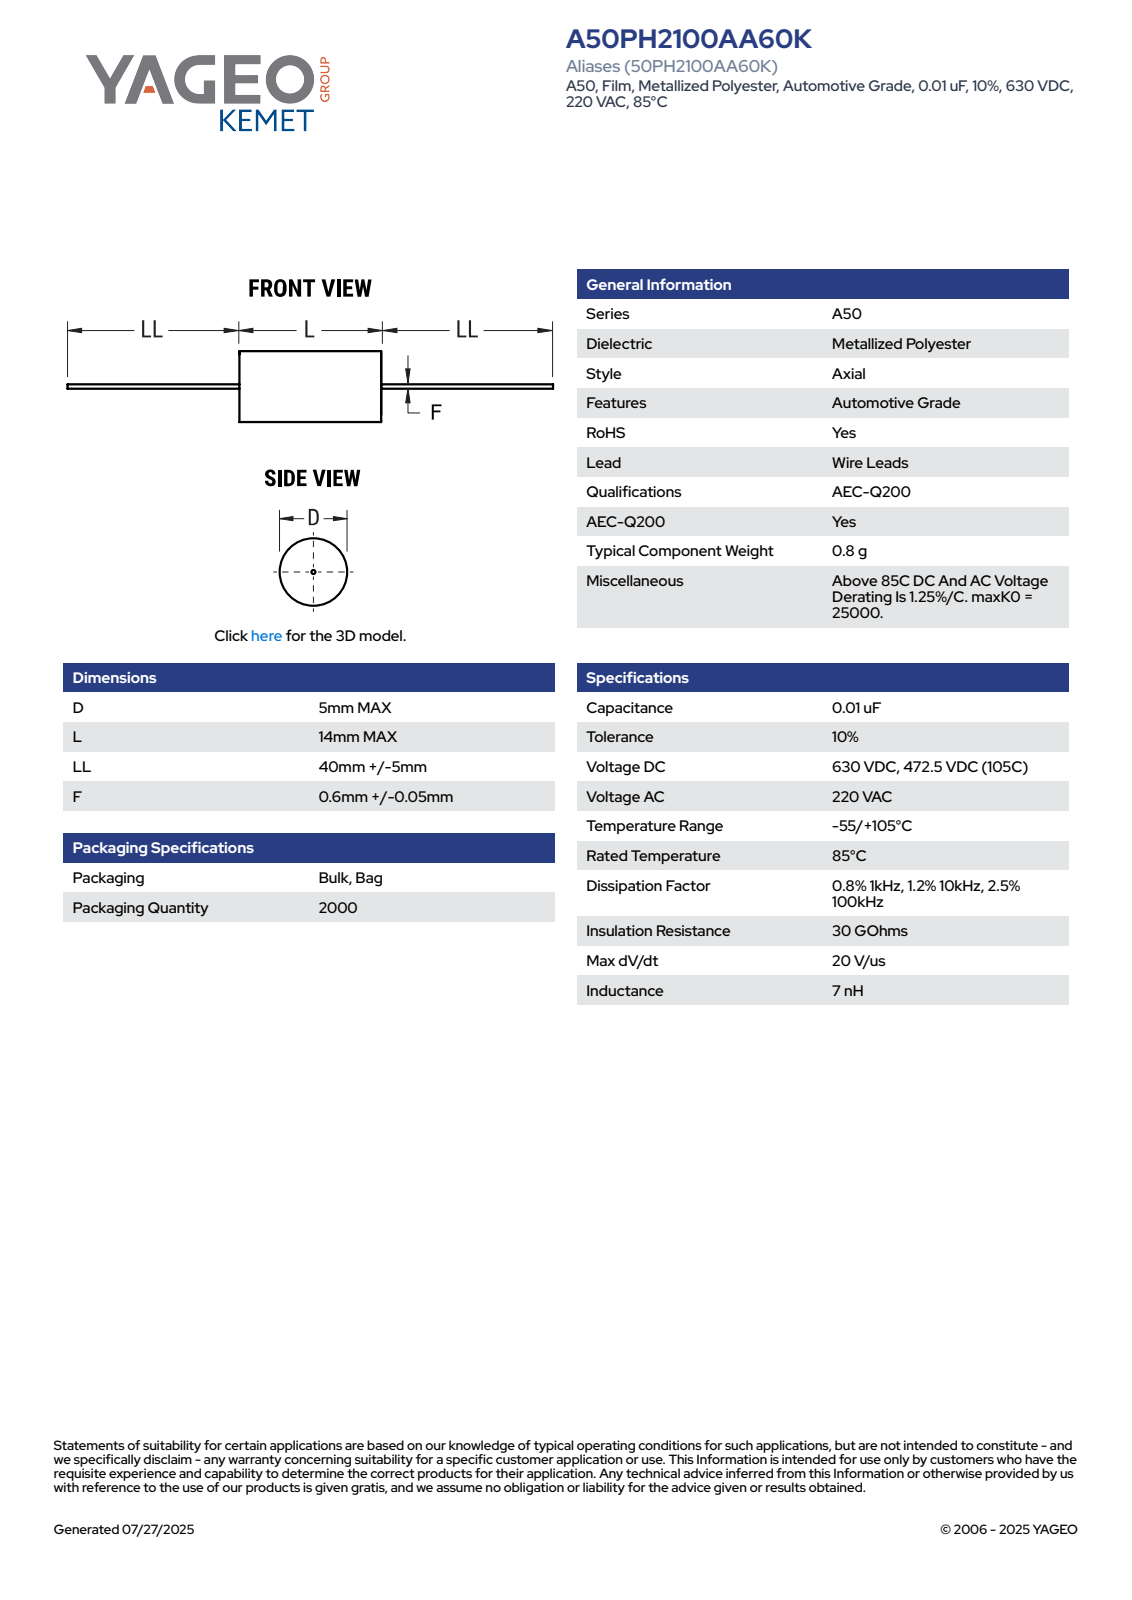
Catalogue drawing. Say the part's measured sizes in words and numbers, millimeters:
The part is named "CFA_ACWF_5X14_D5L14LL45F0.65". Its 3-D file was written by "SolidWorks 2014 (AUTOMOTIVE_DESIGN)". It is 1 solid with 72 faces: 26 planar, 15 cylindrical and 31 other. Overall it measures 104 by 5.01 by 5 millimeters. Its volume is 305 cubic millimeters and its surface area 444 square millimeters. Round bosses or shafts: 1 of diameter 5, 1 of diameter 0.65. Partial cylindrical surfaces (rounded edges, fillets, slot ends): 1 of radius 2.51. The main face-to-face distances are 14, 45, 59, 104.
